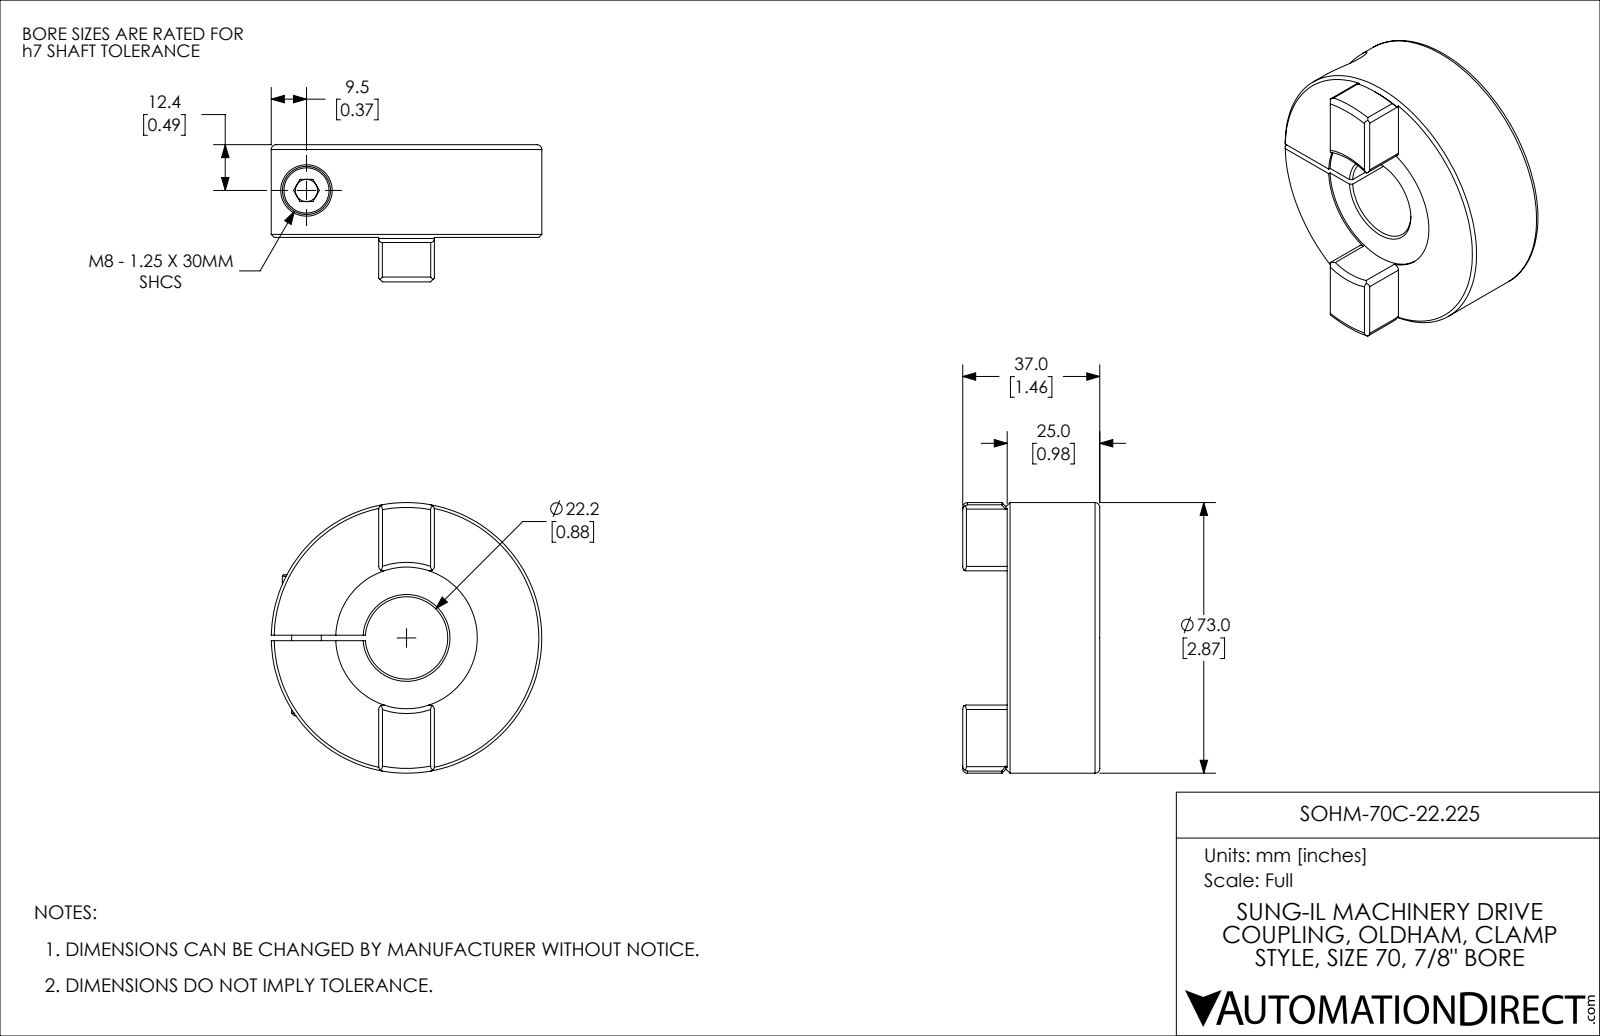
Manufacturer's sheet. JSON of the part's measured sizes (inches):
{"part_name": "SOHM-70C-22.225", "step_written_by": "SolidWorks 2021 (CONFIG_CONTROL_DESIGN)", "units": "inches", "bodies": {"solids": 2, "faces": 93, "planar": 35, "cylindrical": 30, "other": 28}, "overall_size": [2.874, 2.874, 1.457], "volume_in3": 5.999, "surface_area_in2": 31.14, "round_holes": [[0.236, 1], [0.268, 1], [0.335, 1], [0.547, 1], [0.875, 1], [1.504, 1]], "round_bosses_or_shafts": [[2.874, 1], [0.512, 1], [0.315, 1]], "partial_cylinders_radius": [[0.047, 8], [1.969, 1]], "face_to_face_distances": [0.984, 0.965, 0.02, 0.059, 1.457, 0.492, 0.472, 0.591, 0.384, 0.325]}
